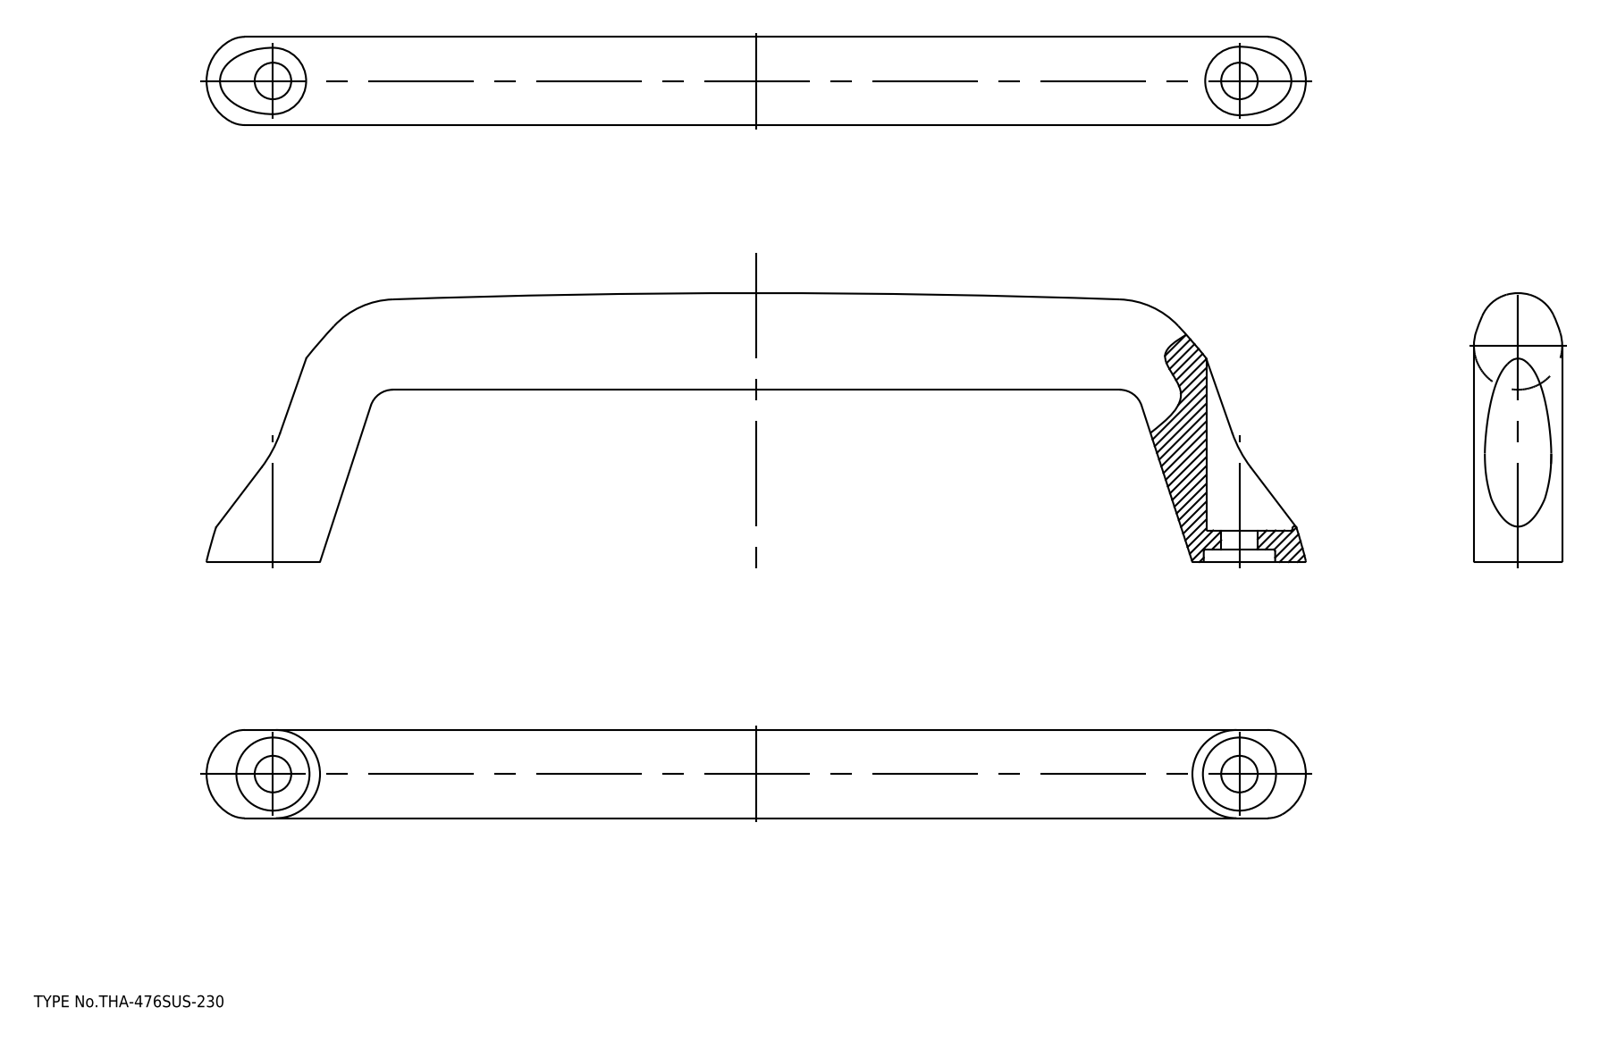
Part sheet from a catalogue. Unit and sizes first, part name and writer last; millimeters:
Units: millimetres
Overall size (bounding box): 261.49 × 64 × 21.34
Round holes (diameter × count): ⌀8.7 ×2, ⌀17.4 ×2
Partial cylindrical surfaces — rounded edges, fillets, slot ends (radius × count): R8.15 ×2
Main face-to-face distances: 7.5, 3, 4.5
Hole centre spacings: 230
Volume: 97 945 mm³ · Surface area: 23 318 mm²
Bodies: 1 solid, 62 faces (6 planar, 10 cylindrical, 46 other)
STEP written by: spGate 20.6.3 (****-****-****-****) (AUTOMOTIVE_DESIGN)
